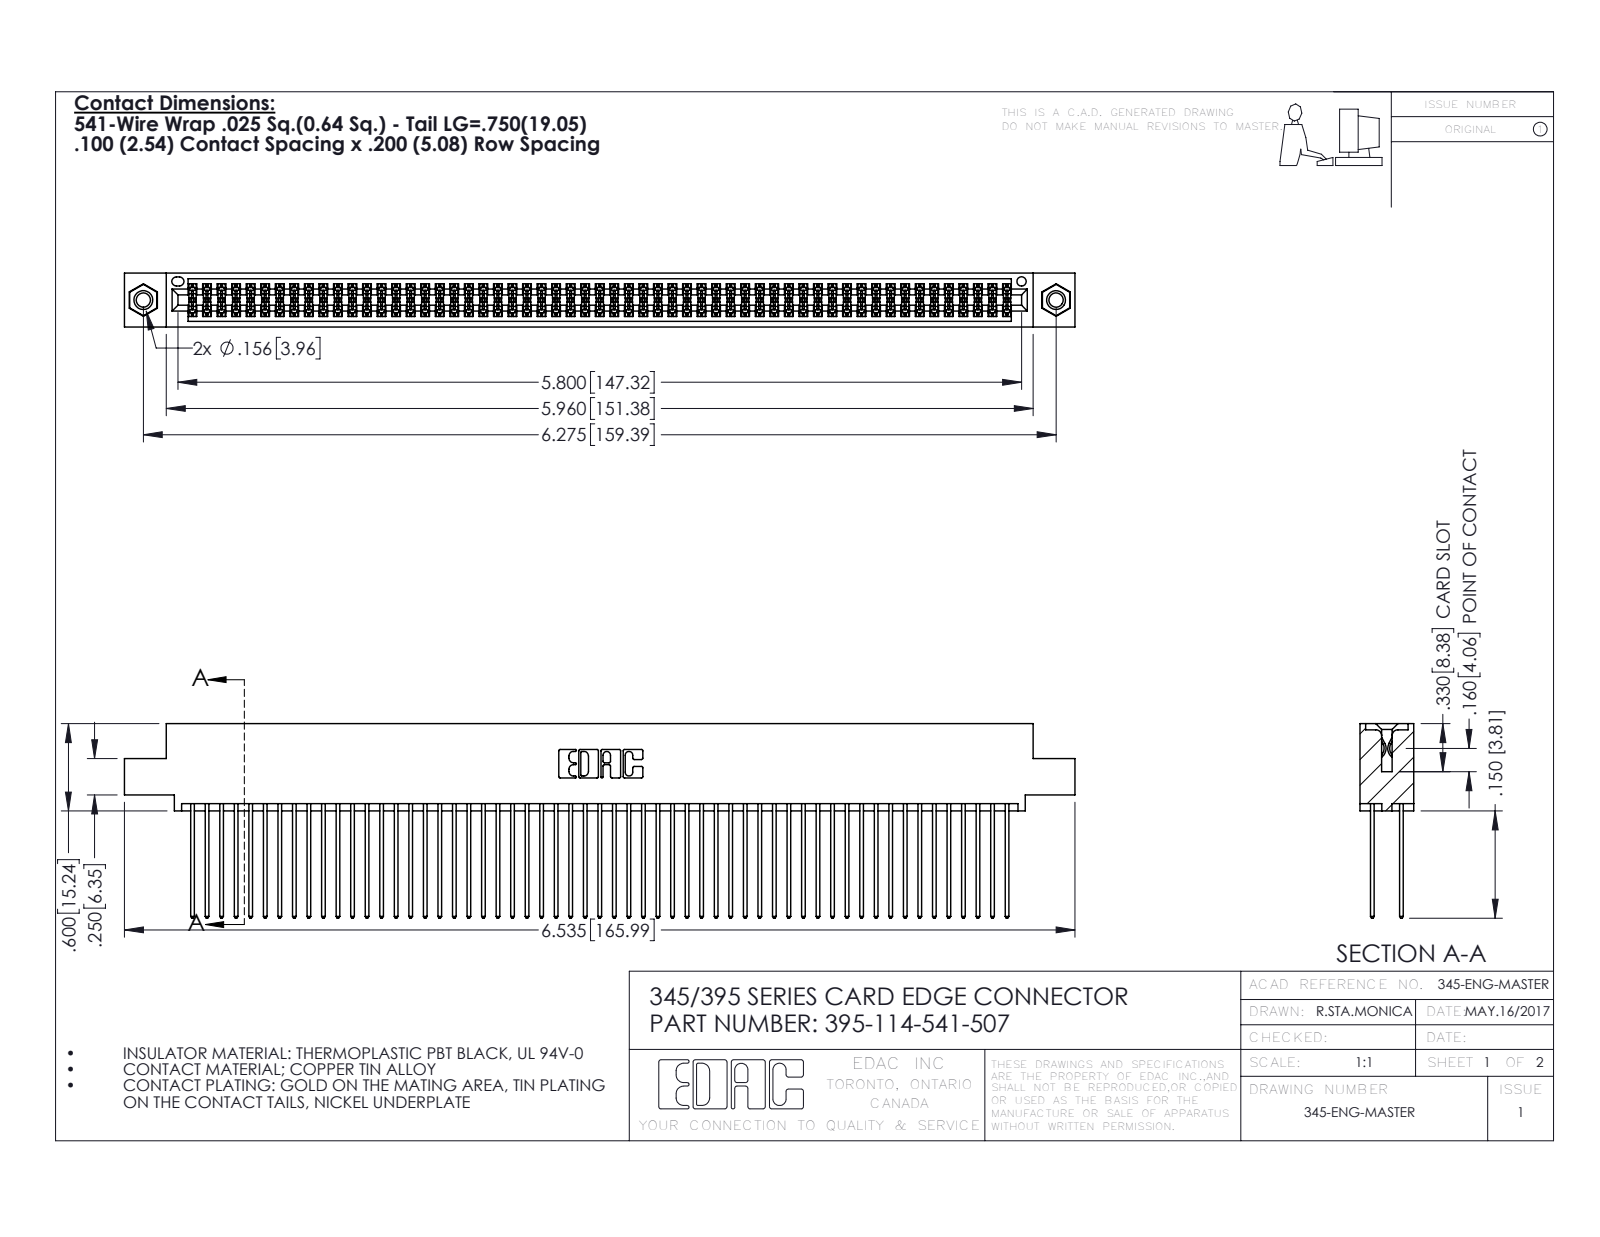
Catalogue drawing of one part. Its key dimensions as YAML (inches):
part_name: "345-250-001_345-250-005-103; 345-292-001_345-293-141; 345 Part_0.110 Offset - 0.156 Dia-TI; 395-114-541-507"
step_written_by: "SolidWorks 2016 (CONFIG_CONTROL_DESIGN)"
units: inches
bodies: {solids: 117, faces: 5890, planar: 3878, cylindrical: 1996, other: 16}
overall_size: [6.535, 1.337, 0.37]
volume: 1.027
surface_area: 43.96
round_holes:
  - {diameter: 0.098, count: 2}
  - {diameter: 0.125, count: 2}
  - {diameter: 0.156, count: 2}
  - {diameter: 0.064, count: 1}
round_bosses_or_shafts:
  - {diameter: 0.155, count: 2}
partial_cylinders:
  - {radius: 0.006, count: 171}
  - {radius: 0.01, count: 114}
  - {radius: 0.01, count: 22}
  - {radius: 0.007, count: 6}
  - {radius: 0.031, count: 6}
  - {radius: 0.026, count: 3}
  - {radius: 0.014, count: 2}
  - {radius: 0.019, count: 2}
face_to_face_distances: [0.072, 0.298, 0.2, 0.098, 0.272, 0.025, 0.225, 0.37, 0.175, 0.149]
hole_center_spacings: [0.27, 6.039, 6.275]
